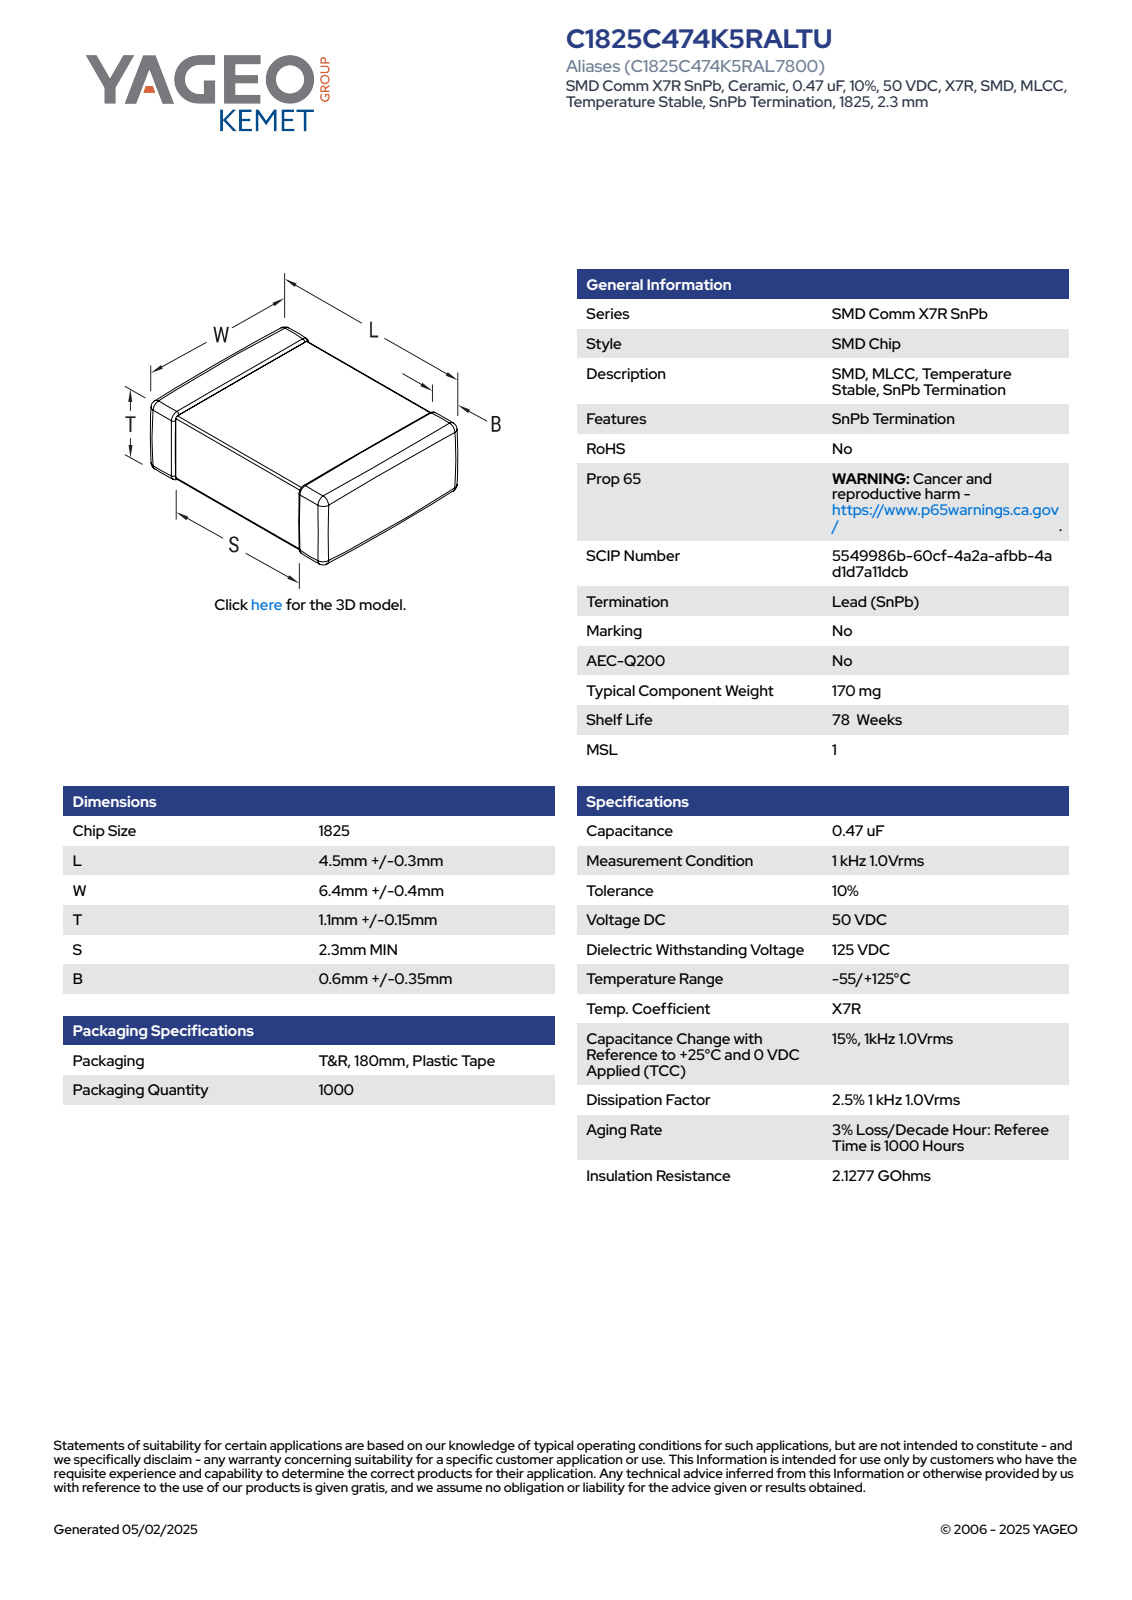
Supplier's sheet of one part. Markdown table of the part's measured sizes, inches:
| quantity | value |
| --- | --- |
| part name | CCS_CCSTDNOS_1825_L4.8W6.8T1.25B0.95 |
| STEP written by | SolidWorks 2014 (AUTOMOTIVE_DESIGN) |
| units | inches |
| bodies | 4 solids, 125 faces (71 planar, 38 cylindrical, 16 other) |
| overall size | 0.268 × 0.189 × 0.049 |
| volume | 0.002 in³ |
| surface area | 0.14 in² |
| partial cylindrical surfaces (radius × count) | 0.006 × 24 |
| main face-to-face distances | 0.038, 0.044, 0.049, 0.189, 0.262, 0.257, 0.268, 0.013, 0.14, 0.135 |
